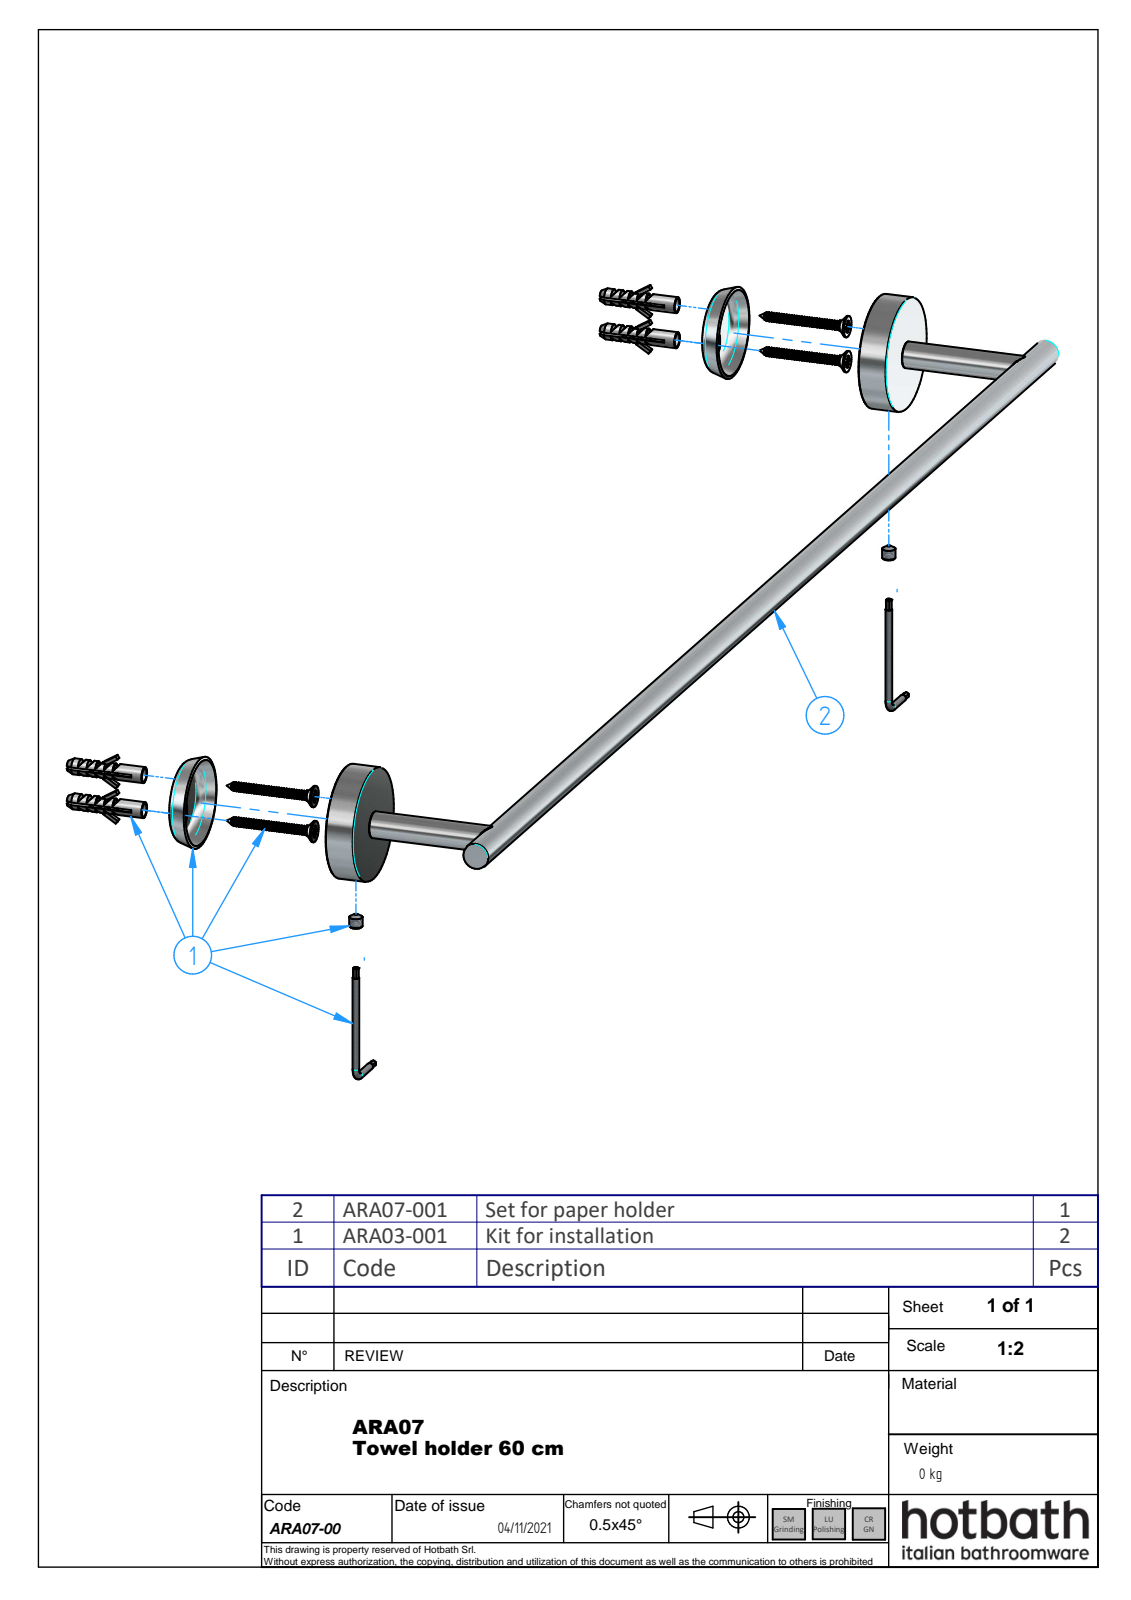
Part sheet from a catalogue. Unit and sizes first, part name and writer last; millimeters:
Units: millimetres
Overall size (bounding box): 603 × 94 × 43
Round holes (diameter × count): ⌀4.13 ×4, ⌀5 ×4, ⌀39.4 ×2, ⌀10 ×1
Round bosses / shafts (diameter × count): ⌀6 ×4, ⌀43 ×2, ⌀10 ×2, ⌀5 ×2
Partial cylindrical surfaces — rounded edges, fillets, slot ends (radius × count): R4.35 ×2, R4.5 ×2, R17.8 ×2
Main face-to-face distances: 1.4, 11, 9.6, 1, 13.8, 2.48, 14.8, 12.8, 560, 4.18
Hole centre spacings: 560, 5.65, 8.15, 13.8, 560.03, 560.06, 560.17
Volume: 64 569 mm³ · Surface area: 38 170 mm²
Bodies: 11 solids, 293 faces (224 planar, 37 cylindrical, 32 other)
Part name (STEP PRODUCT): ARA07-00; ARA03-001_oa_0; CBA01-06; CBA01-07 (+5 more)
STEP written by: ST-DEVELOPER v16.7 (AP242_MANAGED_MODEL_BASED_3D_ENGINEERING_MIM_LF)
